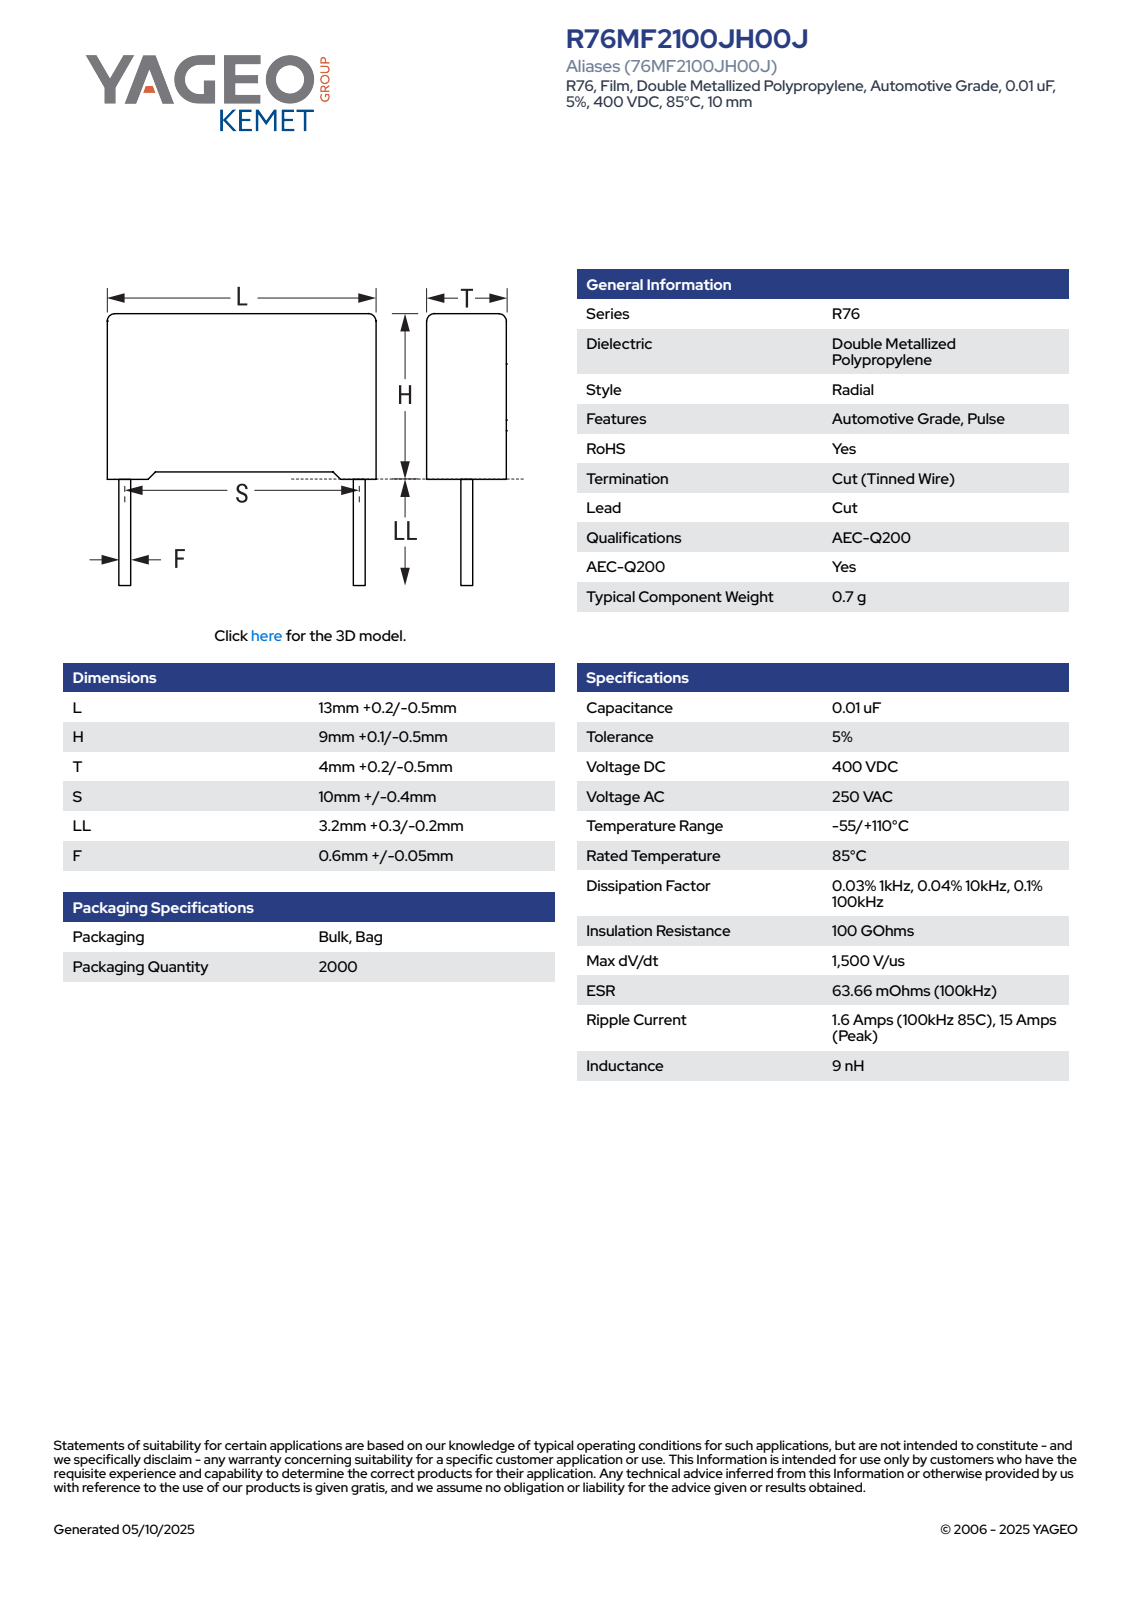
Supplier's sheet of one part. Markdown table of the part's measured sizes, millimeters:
| quantity | value |
| --- | --- |
| part name | CFR_RB2_13X9X4_L13.2H9.1T4.2S10LL3.5F0.65 |
| STEP written by | SolidWorks 2021 (AUTOMOTIVE_DESIGN) |
| units | millimeters |
| bodies | 4 solids, 85 faces (77 planar, 8 cylindrical, 0 other) |
| overall size | 13.2 × 12.6 × 4.21 |
| volume | 473 mm³ |
| surface area | 466 mm² |
| round bosses / shafts (diameter × count) | 0.65 × 2 |
| partial cylindrical surfaces (radius × count) | 0.5 × 4 |
| main face-to-face distances | 4.2, 8.35, 13.2, 0.44, 3.76, 0.75, 9.1, 3.32, 0.31, 8.79 |
